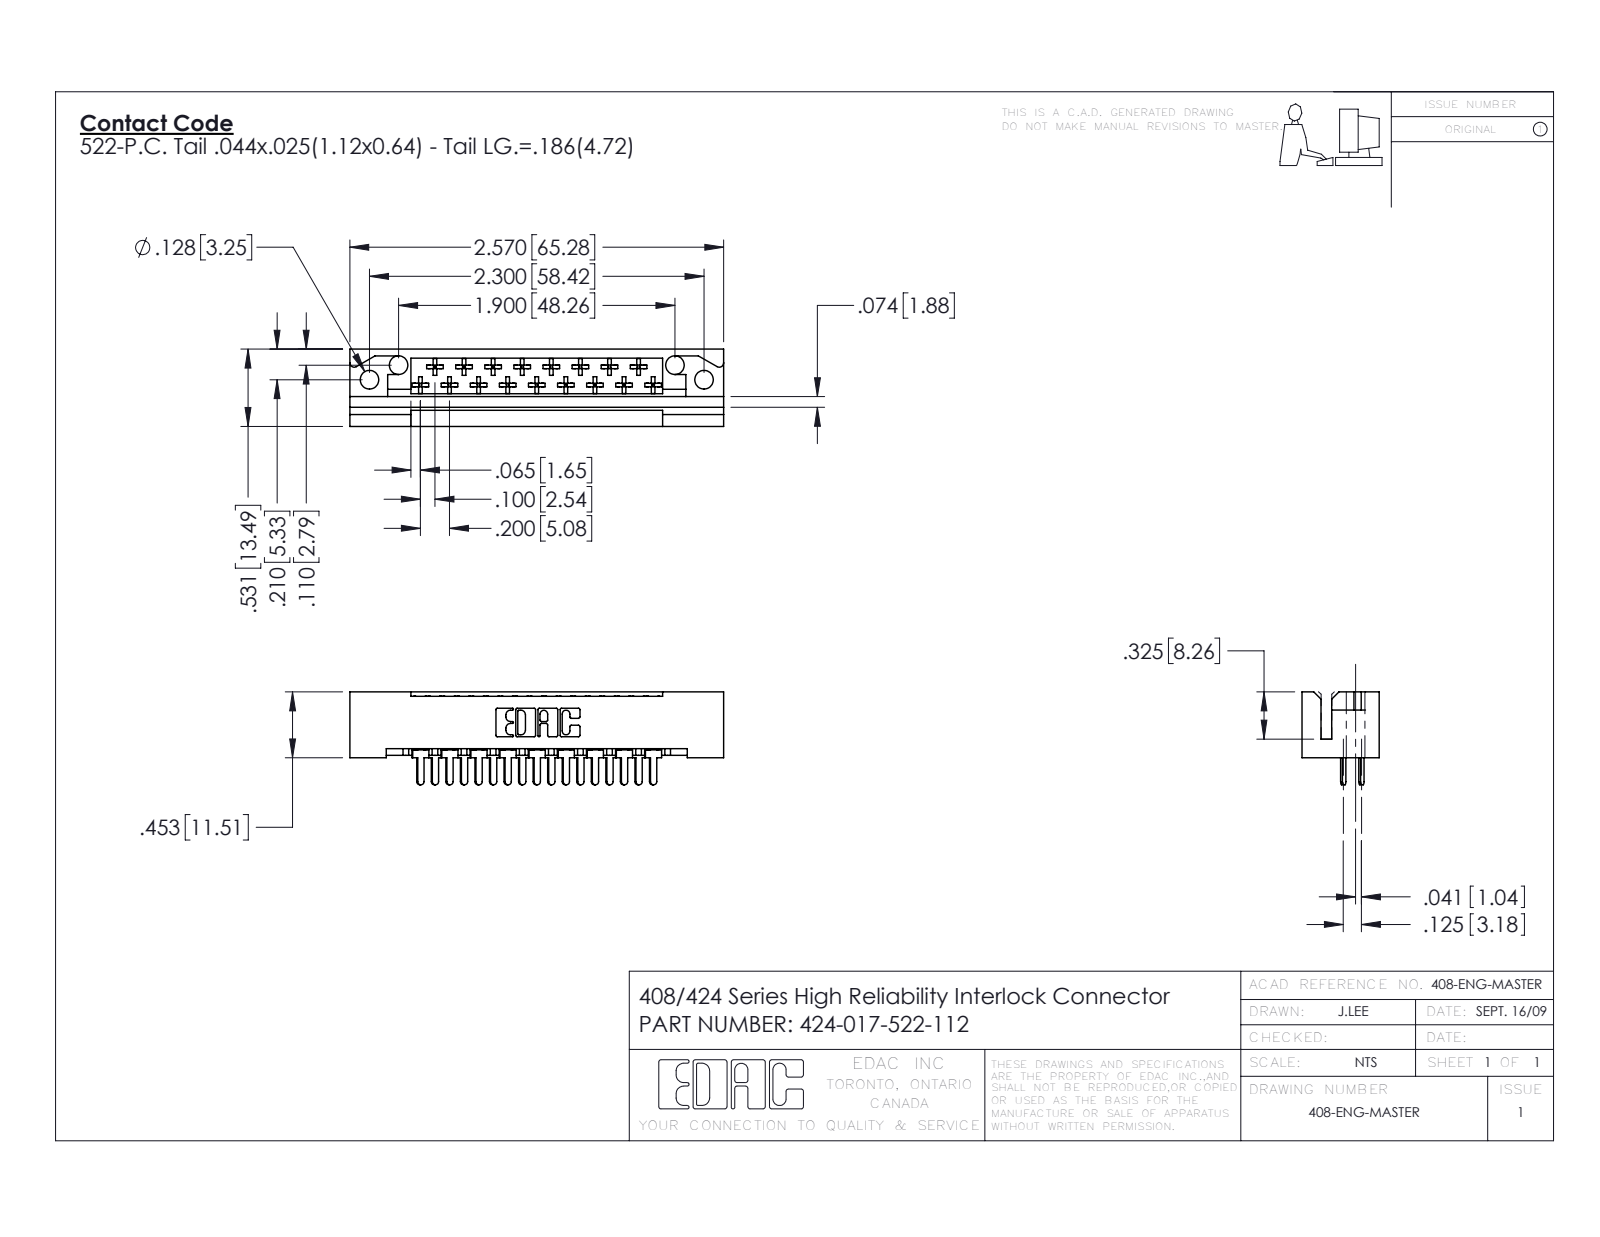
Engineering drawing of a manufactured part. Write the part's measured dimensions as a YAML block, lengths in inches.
part_name: "424-017-522-112; 424 Part_017; 408-290-001_408-290-122"
step_written_by: "SolidWorks 2016 (CONFIG_CONTROL_DESIGN)"
units: inches
bodies: {solids: 18, faces: 1080, planar: 803, cylindrical: 209, other: 68}
overall_size: [2.57, 0.639, 0.531]
volume: 0.432
surface_area: 13.05
round_holes:
  - {diameter: 0.128, count: 4}
partial_cylinders:
  - {radius: 0.01, count: 102}
  - {radius: 0.01, count: 22}
  - {radius: 0.02, count: 19}
  - {radius: 0.022, count: 17}
  - {radius: 0.007, count: 6}
  - {radius: 0.031, count: 6}
  - {radius: 0.026, count: 3}
  - {radius: 0.03, count: 2}
face_to_face_distances: [0.4, 0.025, 0.531, 0.125, 0.1, 0.131, 0.326, 0.074, 0.205, 0.025]
hole_center_spacings: [0.224, 2.102, 1.9, 2.3]
